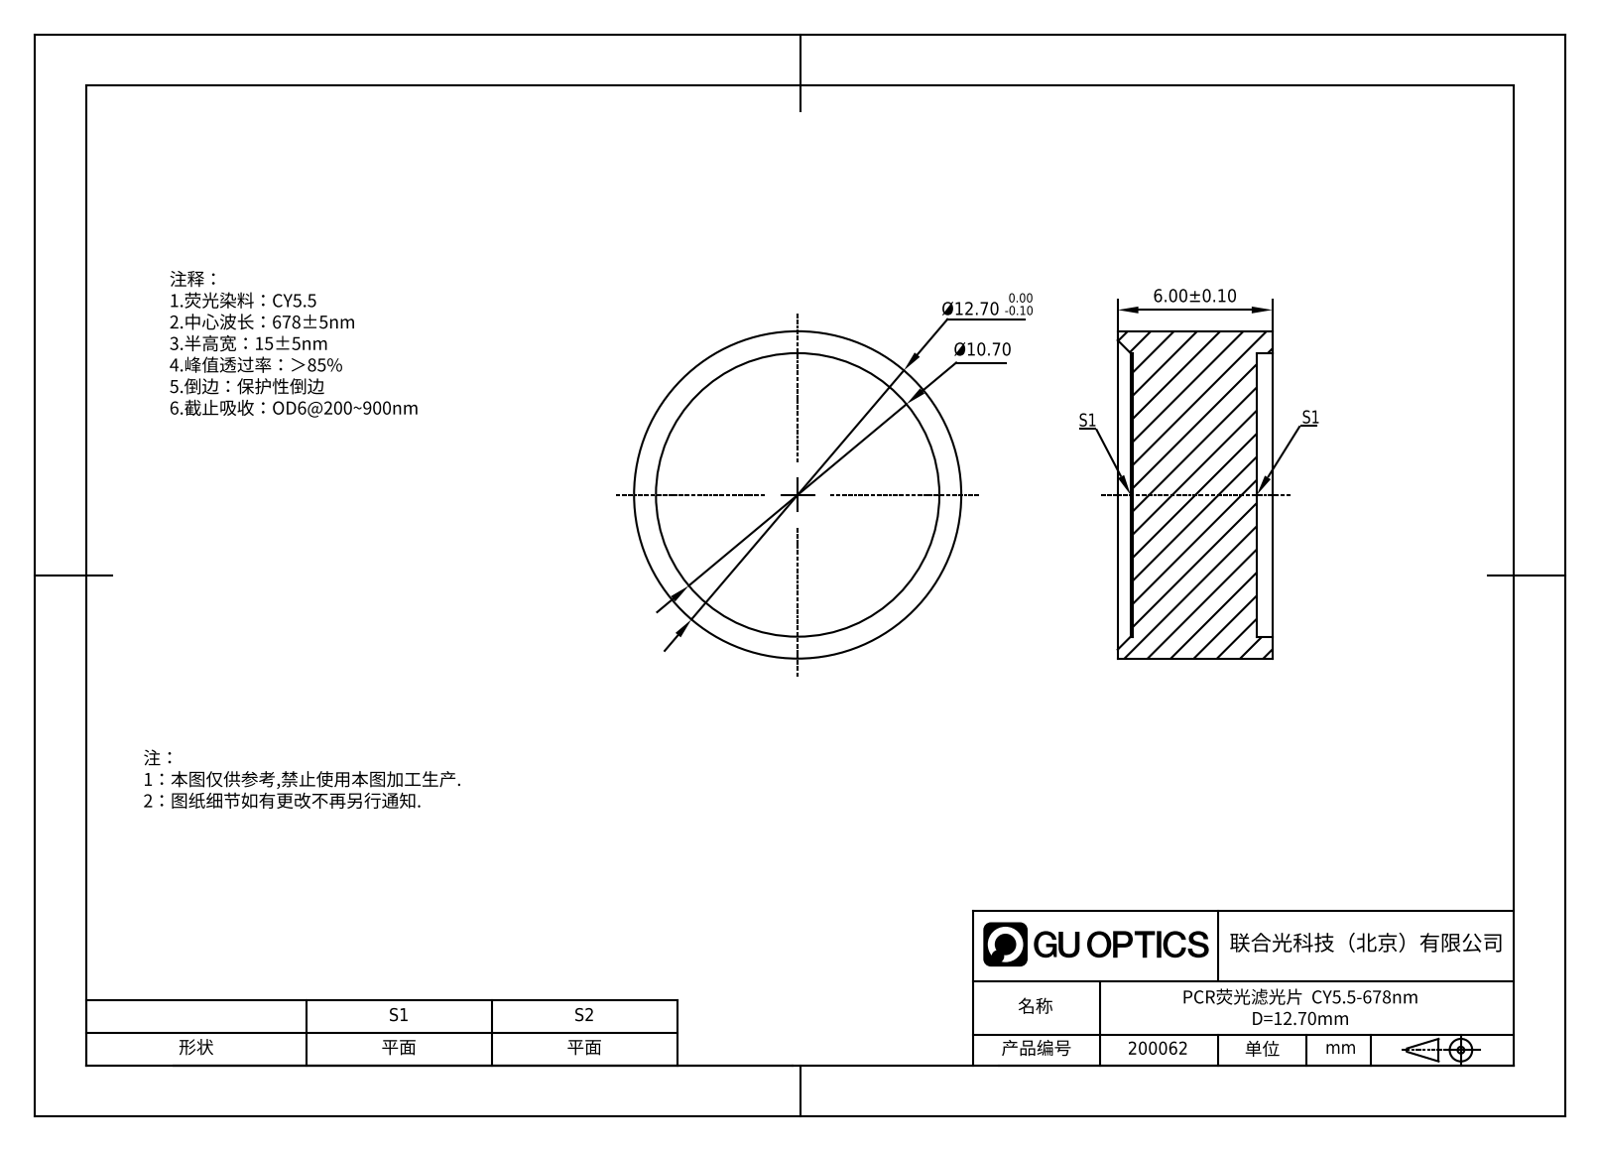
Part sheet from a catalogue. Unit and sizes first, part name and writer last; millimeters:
Units: millimetres
Overall size (bounding box): 12.7 × 12.7 × 6
Round holes (diameter × count): ⌀11 ×1
Round bosses / shafts (diameter × count): ⌀12.7 ×1
Main face-to-face distances: 4.8, 0.6, 5.4, 6
Volume: 642 mm³ · Surface area: 524 mm²
Bodies: 1 solid, 12 faces (4 planar, 6 cylindrical, 2 other)
Part name (STEP PRODUCT): GNIF-030-470-D12
STEP written by: SolidWorks 2022 (AUTOMOTIVE_DESIGN)
